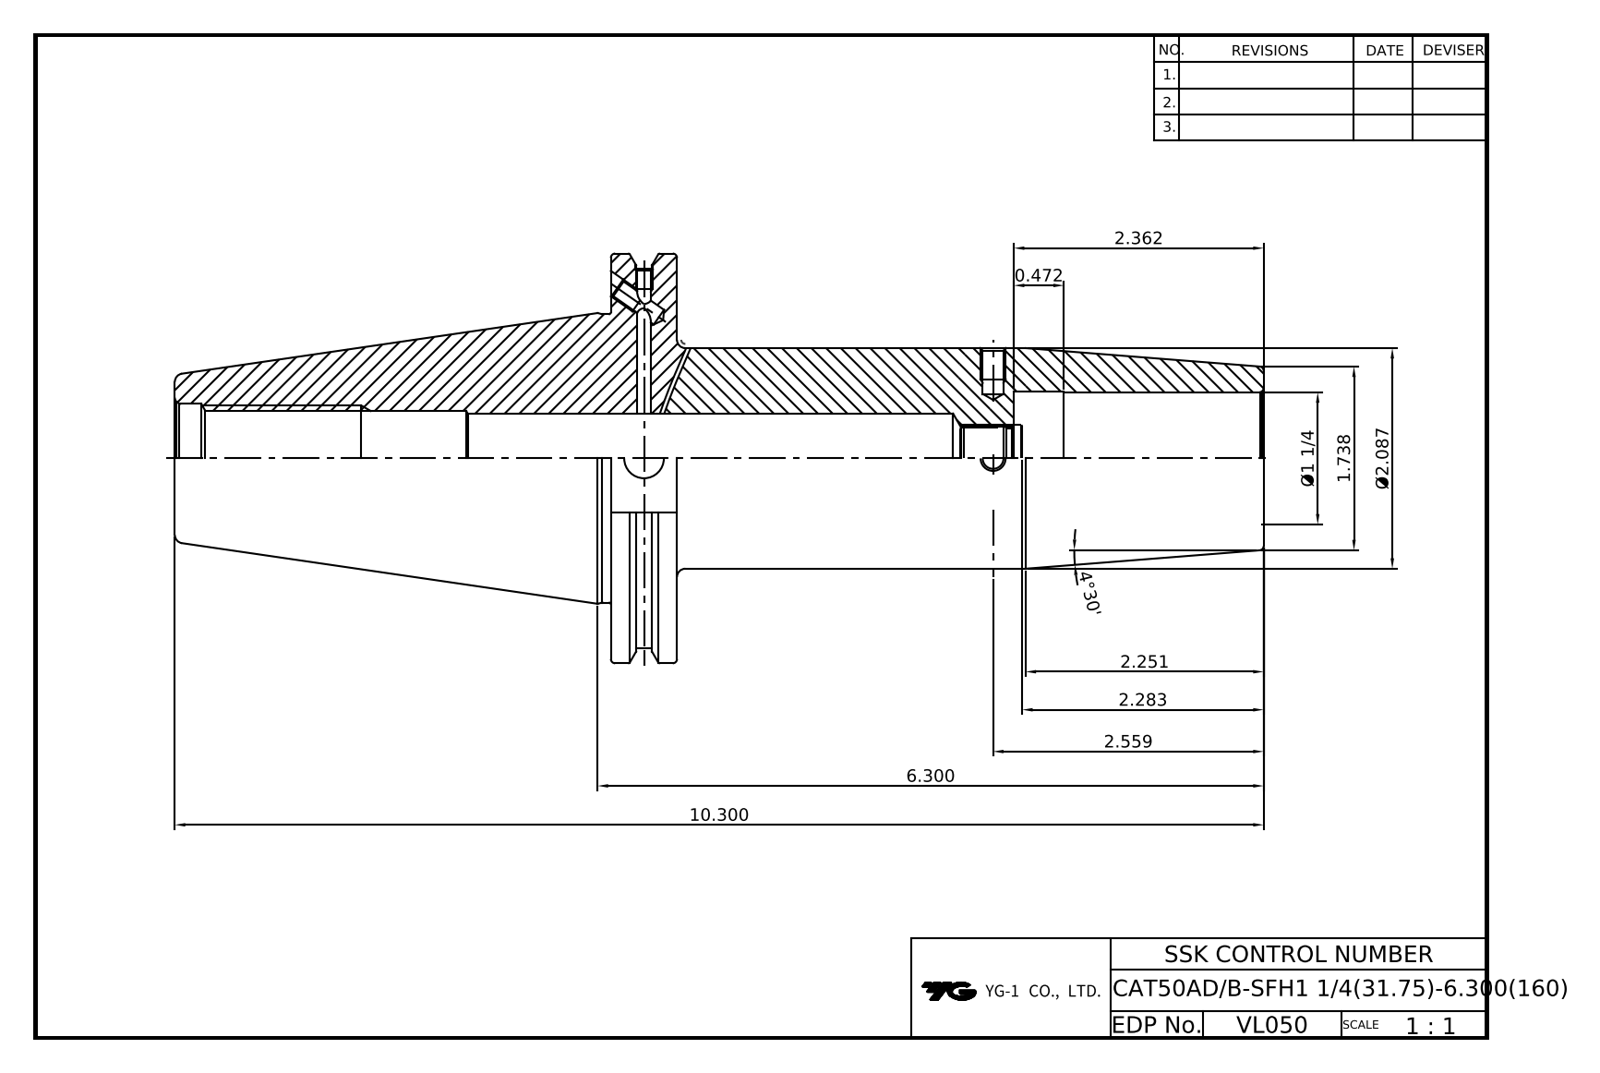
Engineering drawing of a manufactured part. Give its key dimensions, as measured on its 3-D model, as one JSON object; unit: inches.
{"part_name": "VL050-CAT50ADB-SFH31_75-160", "step_written_by": "CREO PARAMETRIC BY PTC INC, 2018100 (CONFIG_CONTROL_DESIGN)", "units": "inches", "bodies": {"solids": 1, "faces": 140, "planar": 42, "cylindrical": 58, "other": 40}, "overall_size": [10.299, 3.875, 3.715], "volume_in3": 32.48, "surface_area_in2": 128.1, "round_holes": [[0.165, 3], [0.197, 2], [0.13, 1], [0.157, 1], [0.375, 1], [0.591, 1], [0.63, 1], [0.846, 1], [0.898, 1], [1, 1], [1.031, 1], [1.25, 1]], "round_bosses_or_shafts": [[3.875, 1], [3.594, 1], [2.726, 1], [2.087, 1]], "face_to_face_distances": [0.626, 3.813, 3.187, 4.124, 4.75, 7.937, 10.299, 6.175, 5.549, 2.362]}
